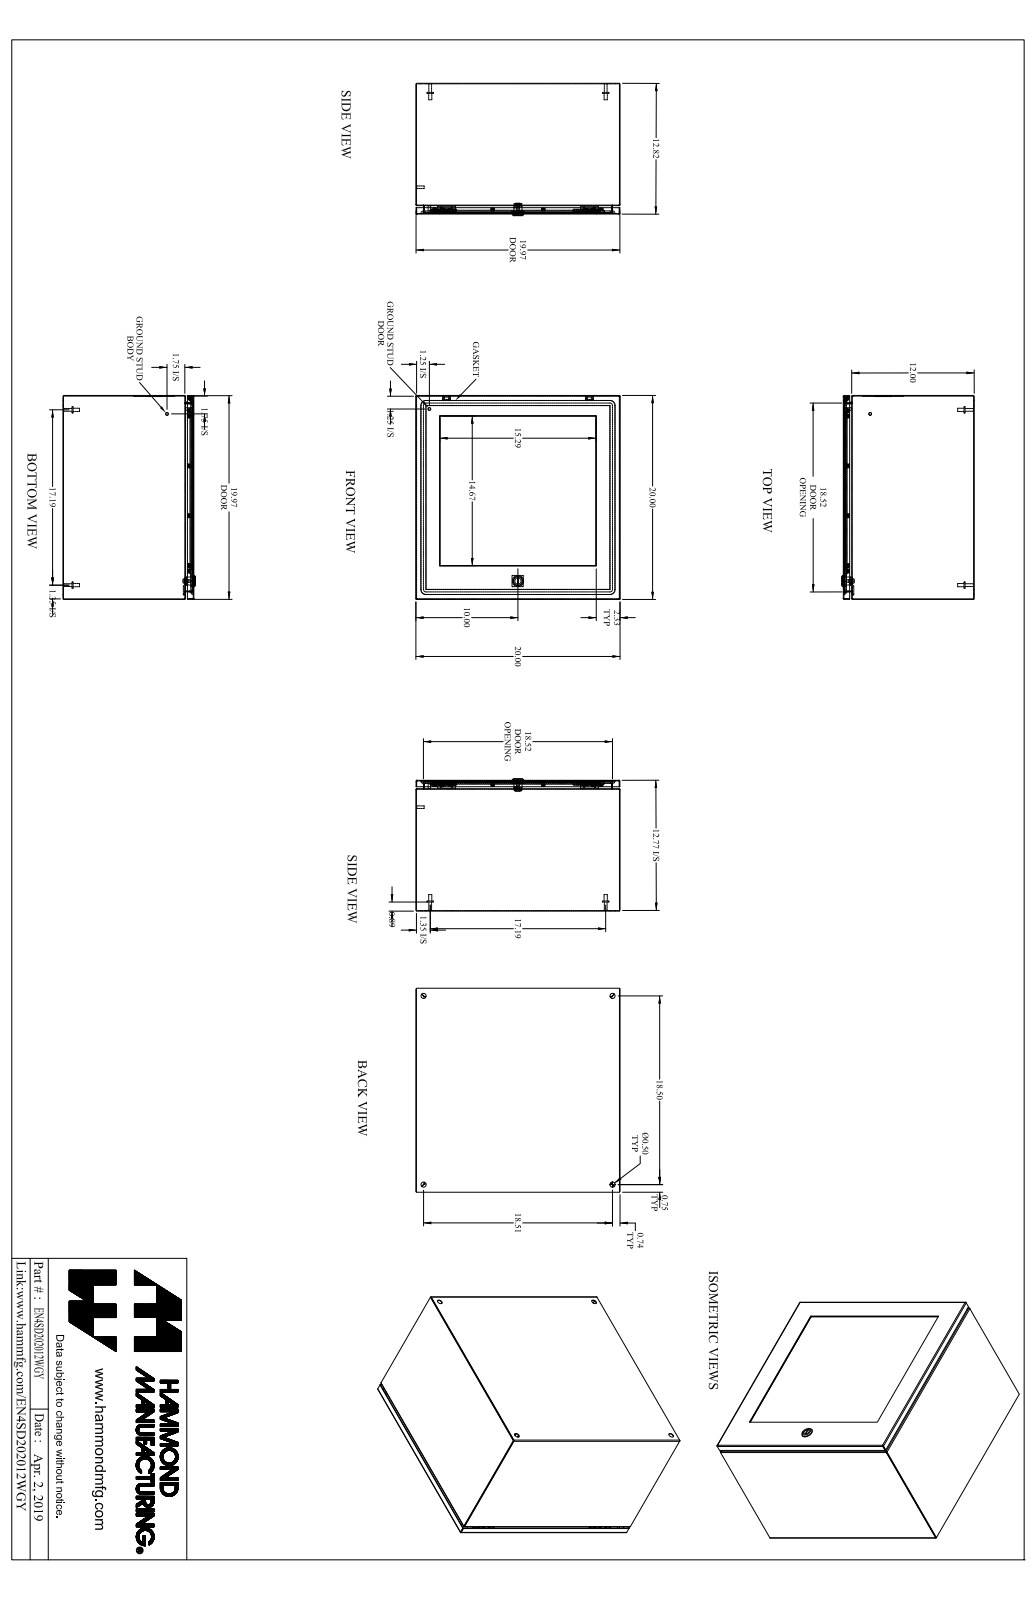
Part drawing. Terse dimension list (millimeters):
name: EN4SD202012WGY_Default
written by: SolidWorks 2019 (CONFIG_CONTROL_DESIGN)
unit: mm
bodies: 66 solids, 1303 faces (664 planar, 385 cylindrical, 254 other)
size: 508 × 508 × 329.7
volume: 2 787 000 mm³; area: 2 748 000 mm²
holes: 16× ⌀3.3, 16× ⌀6.4, 4× ⌀12.7, 1× ⌀4.4, 1× ⌀5.9, 1× ⌀6.1, 1× ⌀6.1, 1× ⌀15.9, 1× ⌀19.9
bosses: 17× ⌀5.7, 16× ⌀9.3, 16× ⌀4.2, 4× ⌀15.9, 4× ⌀8, 4× ⌀6.9, 2× ⌀7.1, 2× ⌀6.4
rounds: 19× R0.7, 19× R2.2, 12× R4.8, 10× R3.2, 4× R0.2, 4× R0.4, 4× R1.6, 4× R2.2
face distances: 1.4, 506.6, 324.2, 505.1, 508, 322.8, 6.4, 316.4, 317.9, 7.8
hole spacings: 125.9, 251.9, 396.5, 126, 251.9, 377.8, 418.4, 418.5
